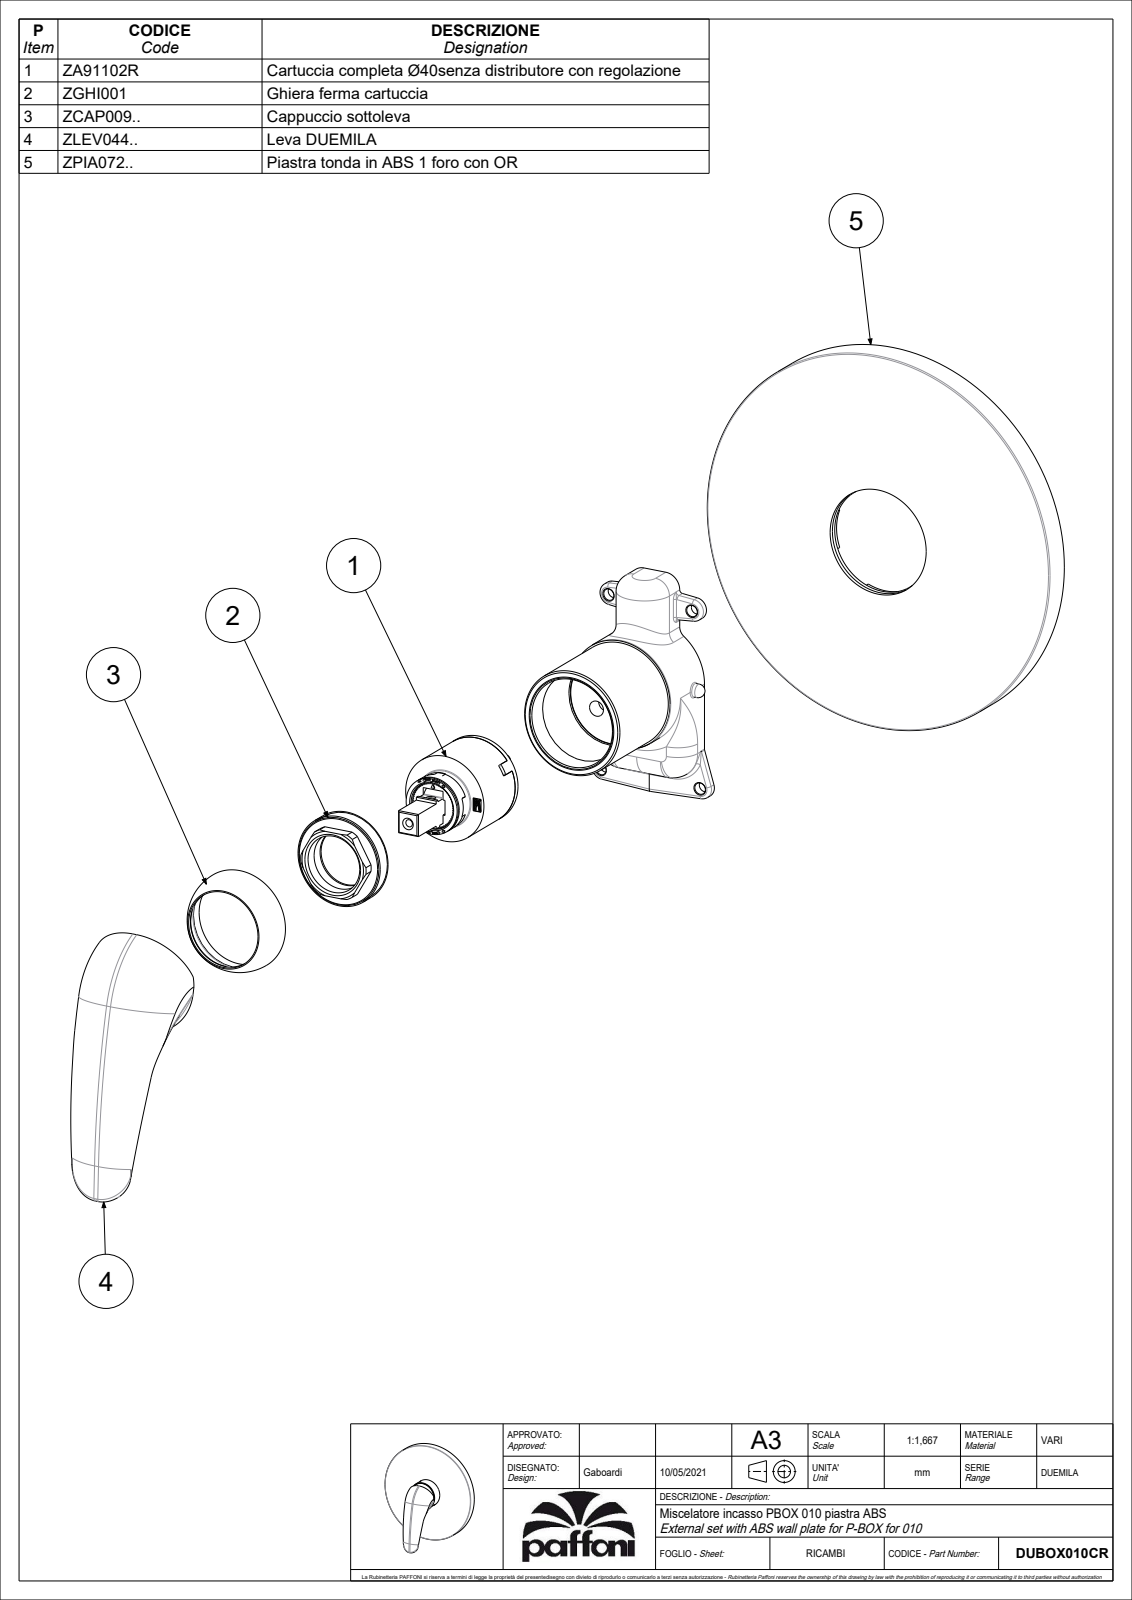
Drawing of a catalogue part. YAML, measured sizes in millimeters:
part_name: "DUBOX010CR"
step_written_by: "CREO PARAMETRIC BY PTC INC, 2020044 (CONFIG_CONTROL_DESIGN)"
units: millimeters
bodies: {solids: 2, faces: 117, planar: 33, cylindrical: 38, other: 46}
overall_size: [178.17, 173, 77.22]
volume: 354297
surface_area: 77428
round_holes:
  - {diameter: 4.5, count: 1}
  - {diameter: 6, count: 1}
  - {diameter: 7.8, count: 1}
  - {diameter: 9.2, count: 1}
  - {diameter: 35, count: 1}
  - {diameter: 40.5, count: 1}
  - {diameter: 40.7, count: 1}
round_bosses_or_shafts:
  - {diameter: 173, count: 1}
  - {diameter: 48.1, count: 1}
  - {diameter: 18.1, count: 1}
  - {diameter: 8, count: 1}
partial_cylinders:
  - {radius: 1.5, count: 2}
  - {radius: 15, count: 2}
  - {radius: 24, count: 2}
  - {radius: 24.5, count: 2}
  - {radius: 18, count: 1}
  - {radius: 39.04, count: 1}
  - {radius: 340.59, count: 1}
  - {radius: 341.58, count: 1}
face_to_face_distances: [13, 10.1, 43.2, 30.2, 34.7, 21.7, 8.5, 10.6, 31.2, 18.2]
